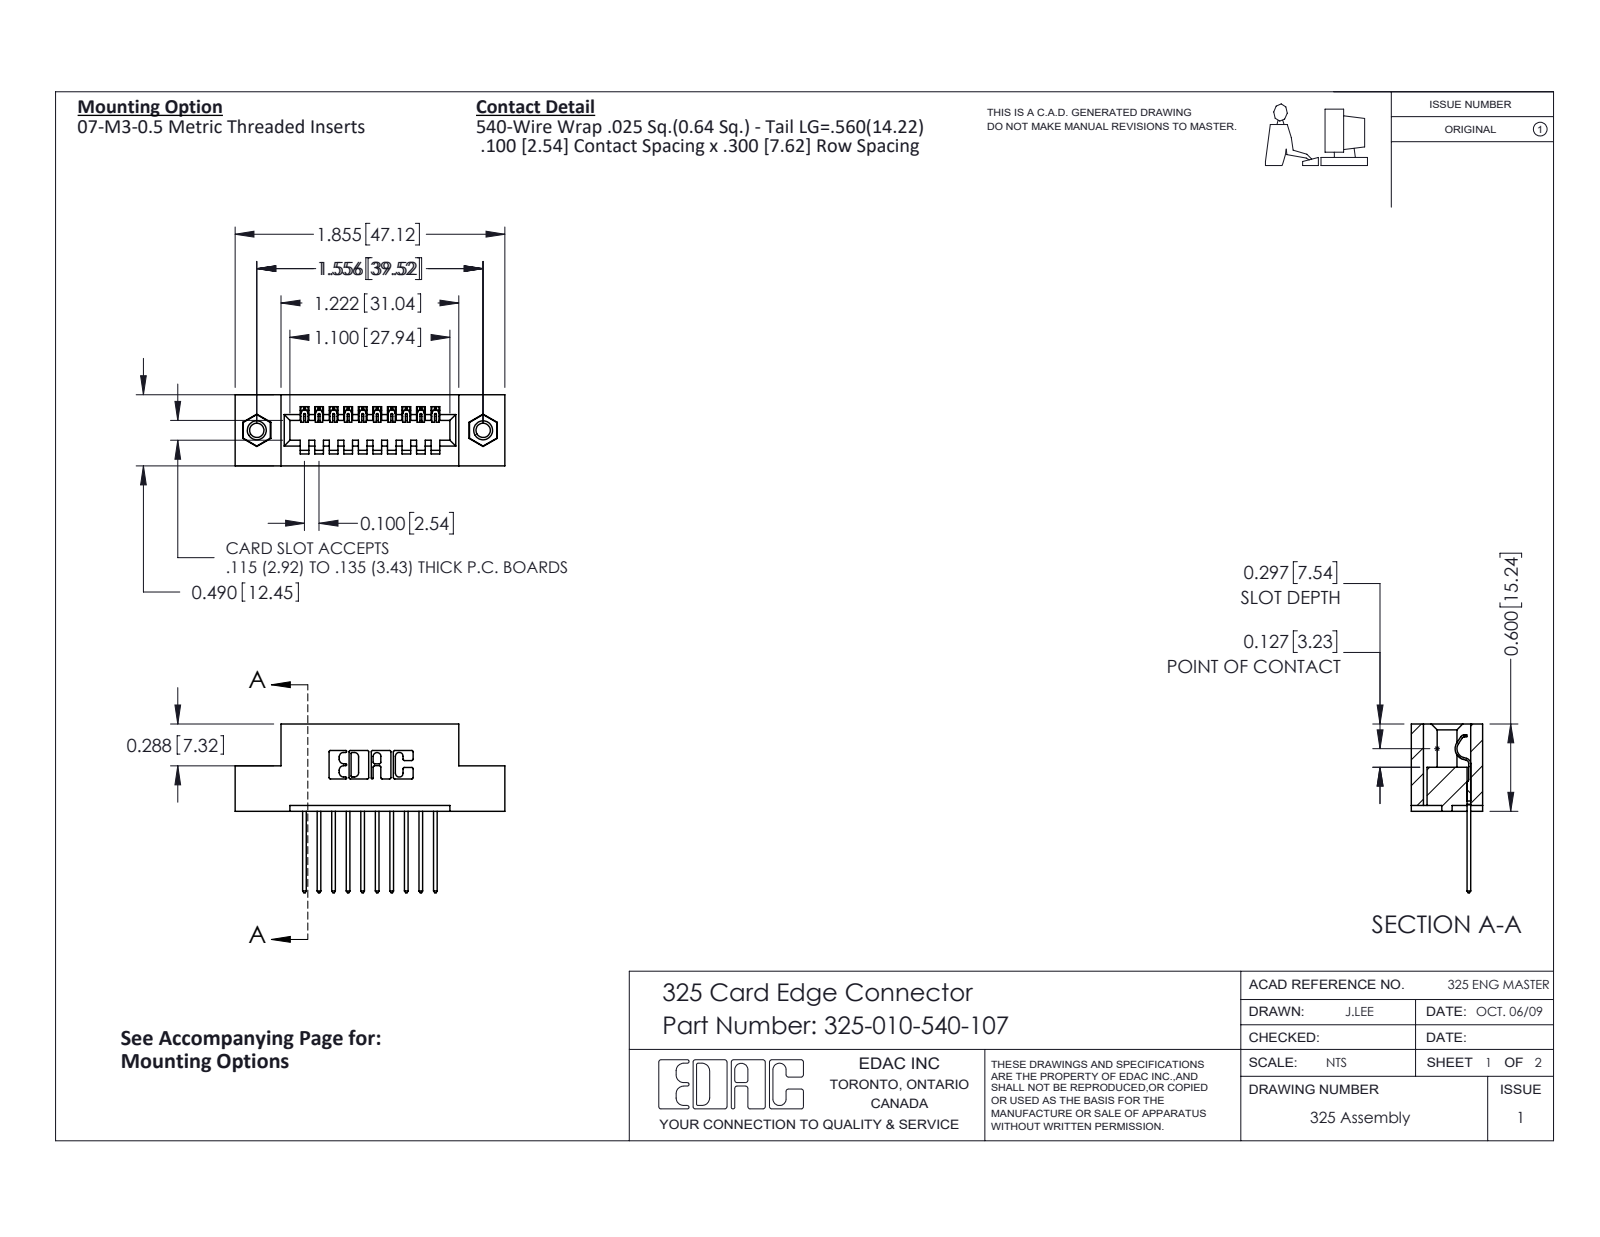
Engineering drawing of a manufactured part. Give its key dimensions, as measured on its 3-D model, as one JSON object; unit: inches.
{"part_name": "325-010-540-107; 325-292-001_325-293-140; 345-250-001_345-250-005-103; 325 Part_TI", "step_written_by": "SolidWorks 2016 (CONFIG_CONTROL_DESIGN)", "units": "inches", "bodies": {"solids": 13, "faces": 754, "planar": 522, "cylindrical": 216, "other": 16}, "overall_size": [1.855, 1.16, 0.49], "volume_in3": 0.35, "surface_area_in2": 9.059, "round_holes": [[0.098, 2], [0.125, 2], [0.16, 2]], "round_bosses_or_shafts": [[0.155, 2]], "partial_cylinders_radius": [[0.01, 22], [0.006, 20], [0.01, 20], [0.007, 6], [0.031, 6], [0.026, 3], [0.014, 1], [0.022, 1]], "face_to_face_distances": [0.3, 0.083, 0.407, 0.49, 0.04, 0.1, 0.2, 0.6, 0.4, 0.107], "hole_center_spacings": [1.556]}
